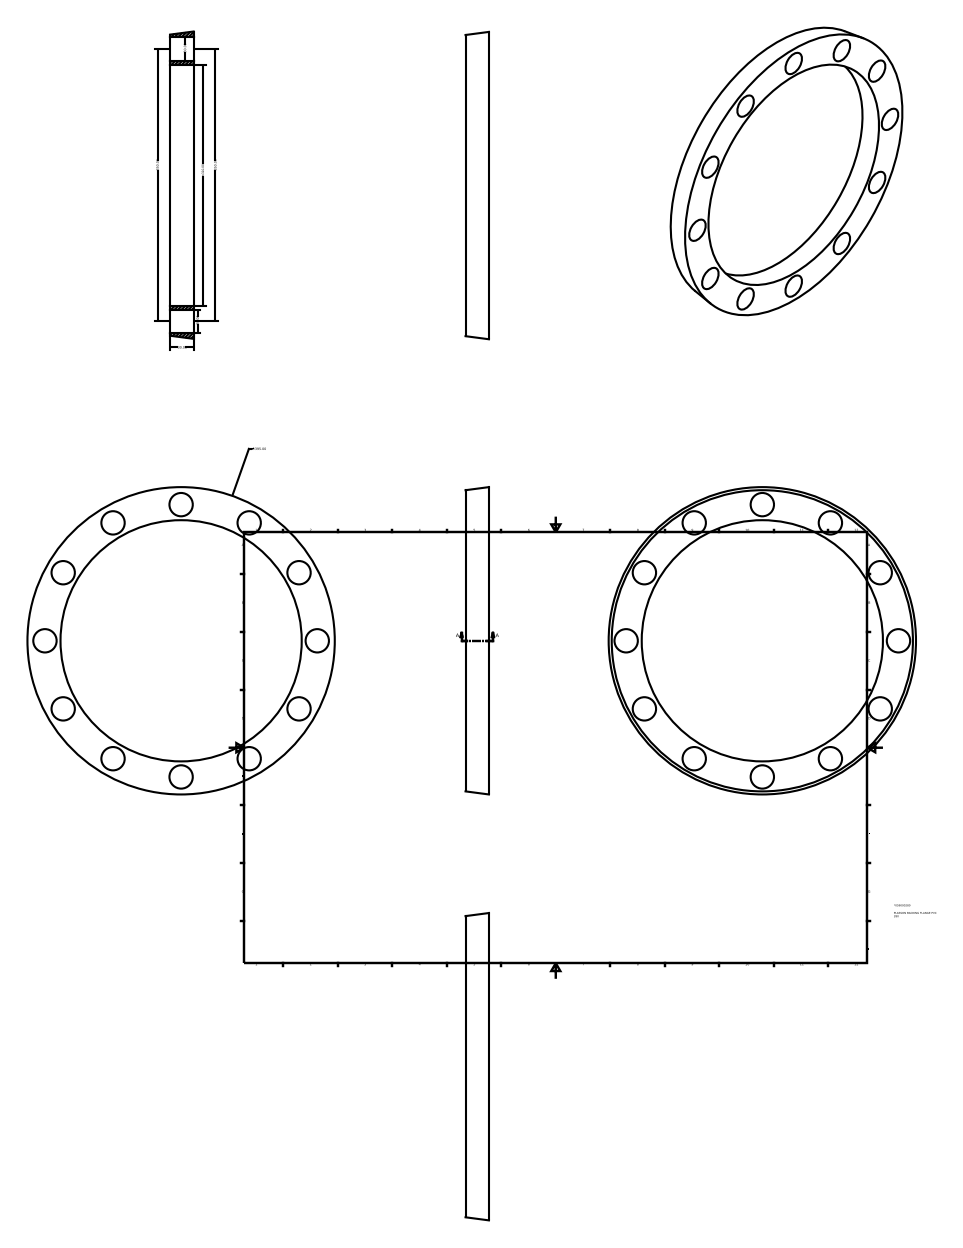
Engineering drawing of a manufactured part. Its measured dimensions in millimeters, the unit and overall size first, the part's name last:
Units: millimetres
Overall size (bounding box): 395 × 395 × 30
Round holes (diameter × count): ⌀30 ×12, ⌀310 ×1
Main face-to-face distances: 30
Hole centre spacings: 175, 338.07, 90.59, 247.48, 303.11, 90.58, 247.49, 303.1
Volume: 1 084 000 mm³ · Surface area: 172 632 mm²
Bodies: 1 solid, 16 faces (2 planar, 13 cylindrical, 1 other)
Part name (STEP PRODUCT): (_AS)059000280
STEP written by: Autodesk Inventor 2015 (AUTOMOTIVE_DESIGN)
